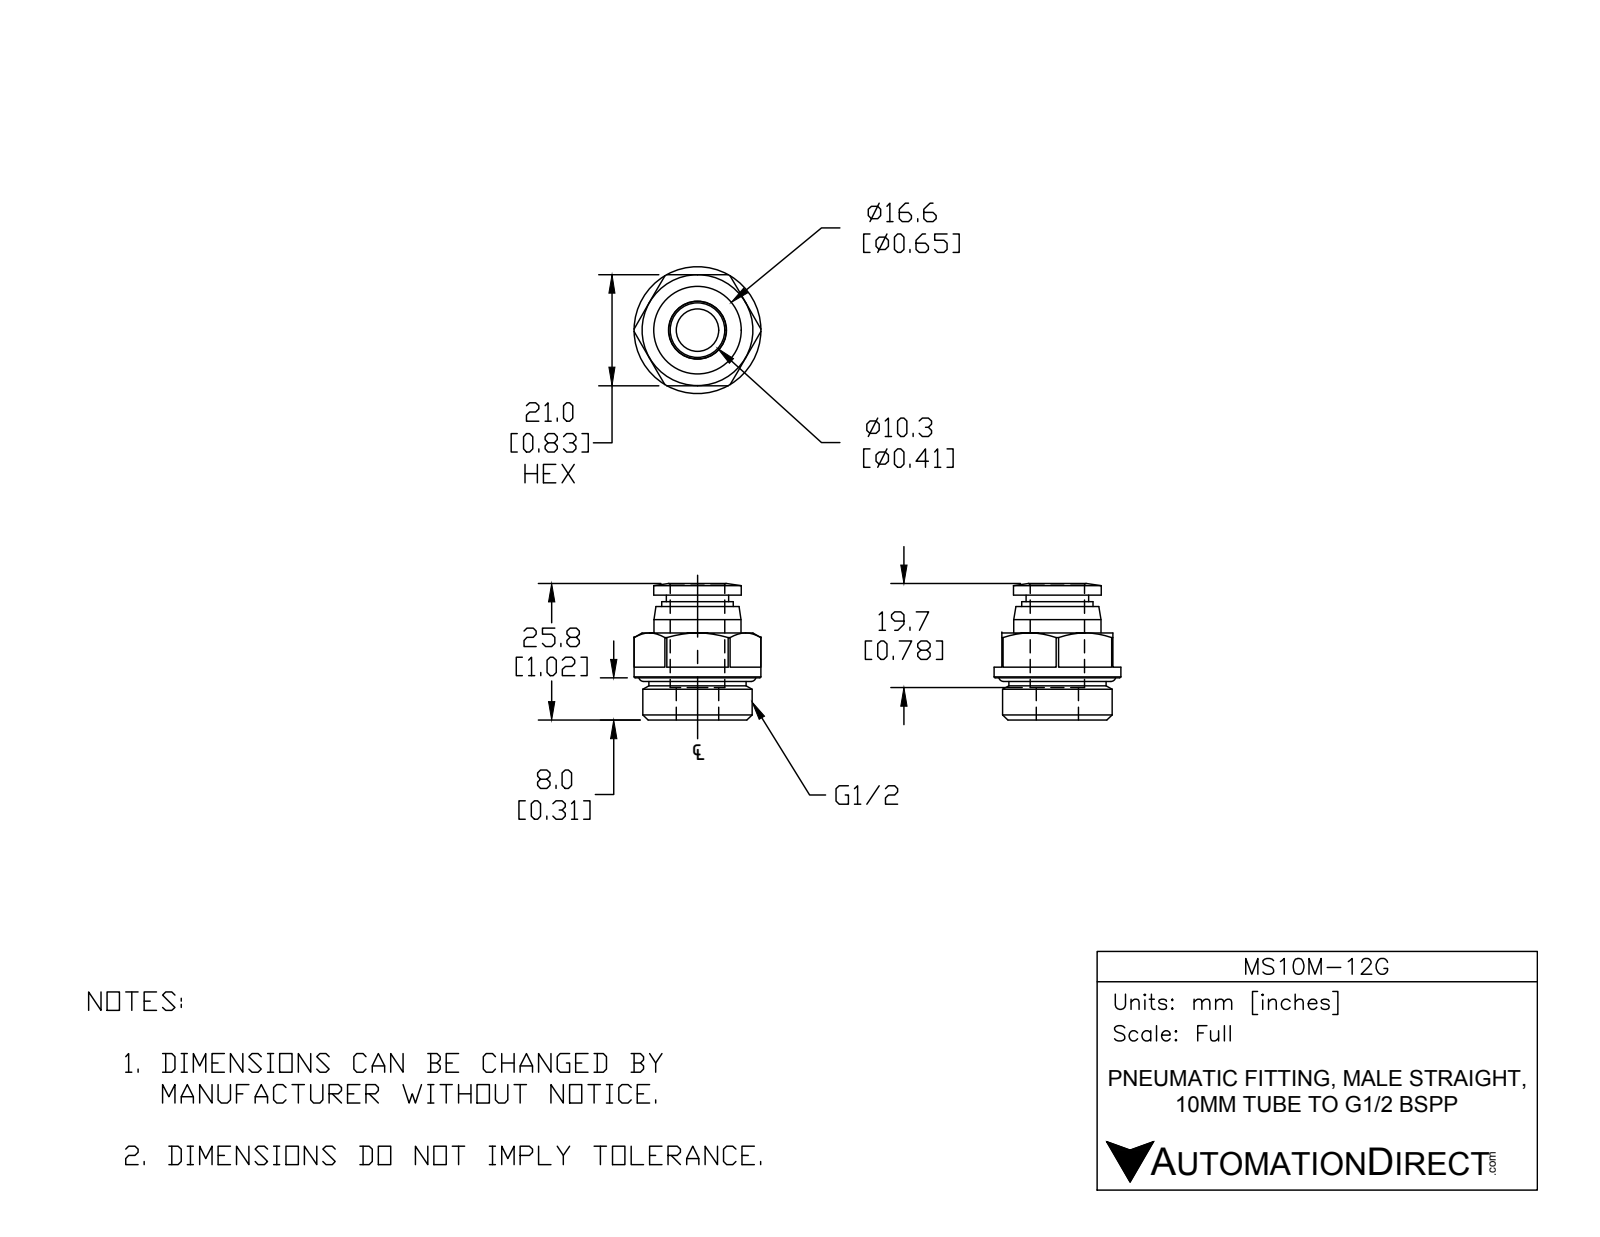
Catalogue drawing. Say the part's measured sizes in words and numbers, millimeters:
The part is named "MS10M-12G". Its 3-D file was written by "SolidWorks 2018 (AUTOMOTIVE_DESIGN)". It is 2 solids with 64 faces: 21 planar, 18 cylindrical and 25 other. Overall it measures 25.9 by 24 by 24 millimeters. Its volume is 5 780 cubic millimeters and its surface area 3 865 square millimeters. Round holes: 1 of diameter 8, 1 of diameter 10.3. Round bosses or shafts: 1 of diameter 24, 1 of diameter 20.7, 1 of diameter 18.4, 1 of diameter 16.6, 1 of diameter 16.5, 1 of diameter 13.5, 1 of diameter 11.8. The main face-to-face distances are 21, 16.5, 23.6, 7.1, 10, 6.5, 13.6, 21.5, 11.5, 5.
